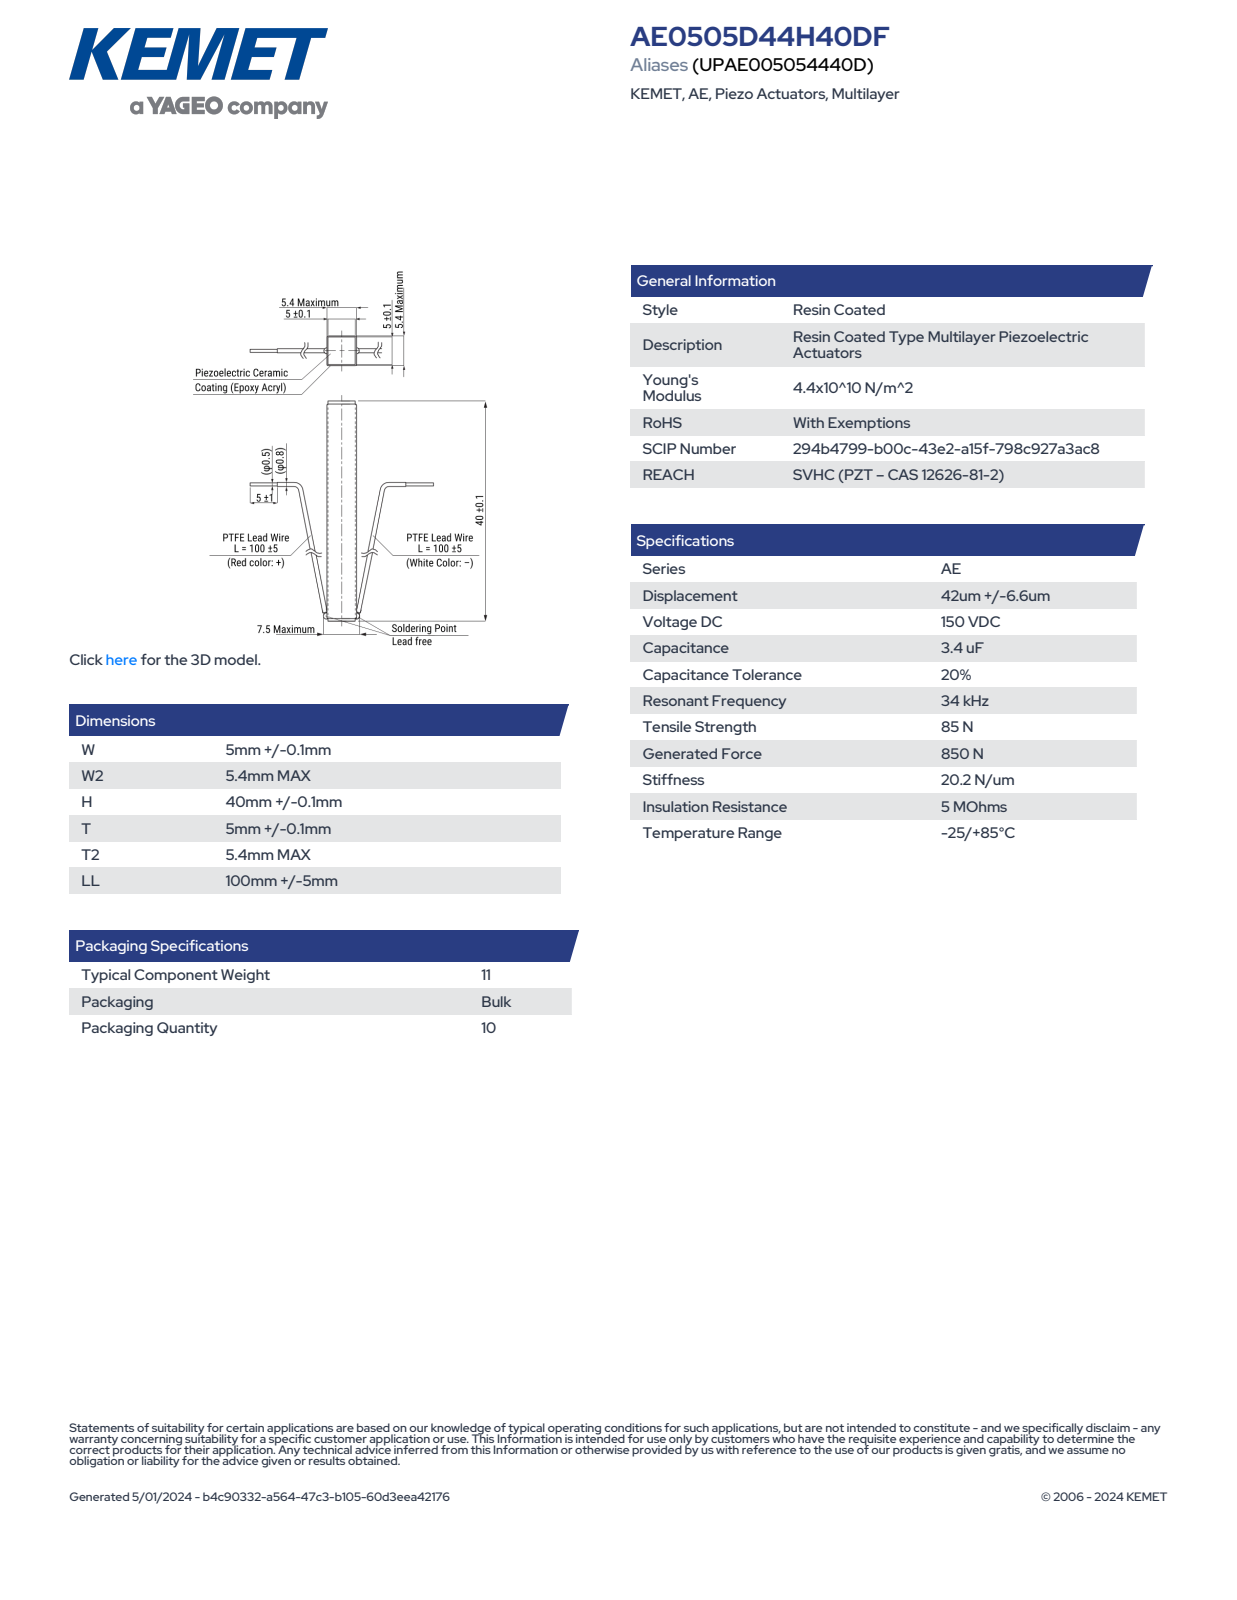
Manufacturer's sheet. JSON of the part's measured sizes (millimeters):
{"part_name": "AL_KAE2_W5.1W25.4H40.1T5.1T25.4", "step_written_by": "SolidWorks 2020 (AUTOMOTIVE_DESIGN)", "units": "millimeters", "bodies": {"solids": 4, "faces": 93, "planar": 85, "cylindrical": 8, "other": 0}, "overall_size": [40.1, 5.4, 5.4], "volume_mm3": 1043, "surface_area_mm2": 886, "partial_cylinders_radius": [[0.15, 8]], "face_to_face_distances": [5.1, 5, 5.25, 4.9, 5.4, 40.1, 16.12, 23.98, 3.93, 36.17]}
